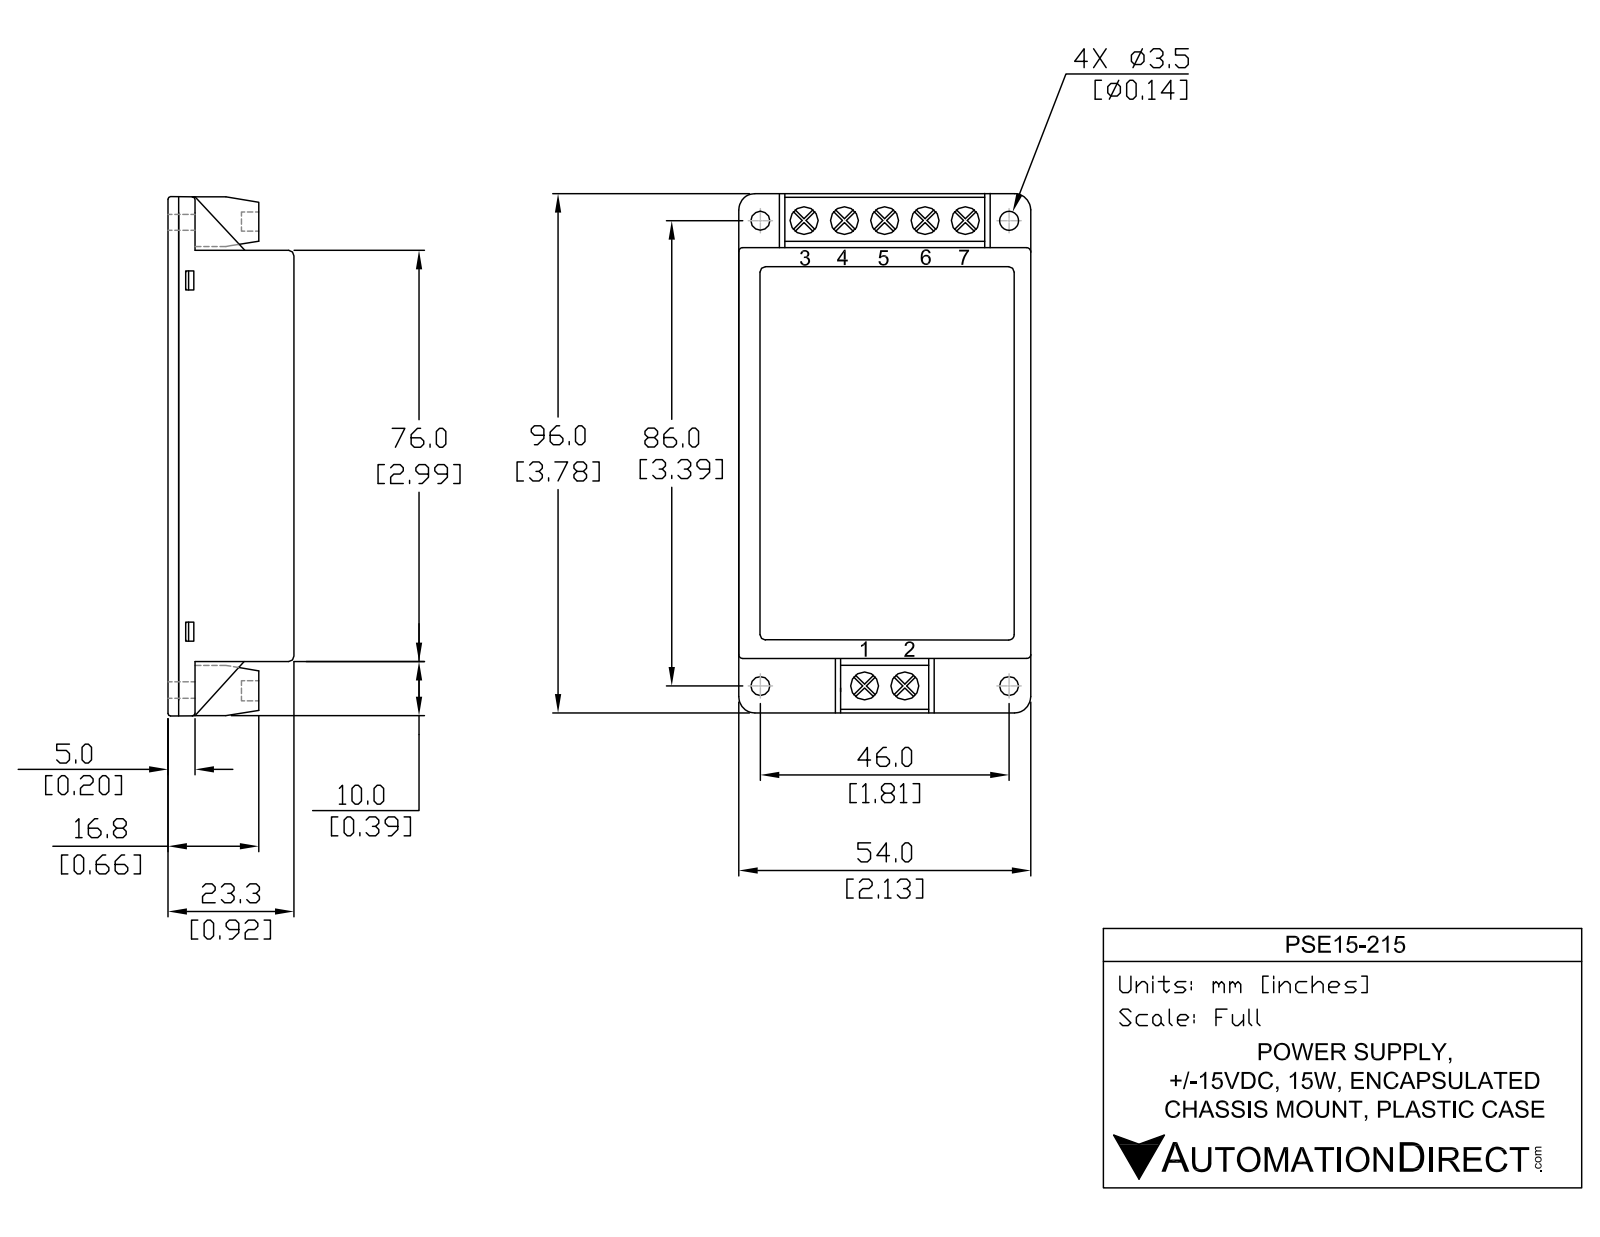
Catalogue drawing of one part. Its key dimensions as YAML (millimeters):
part_name: "PSE15-215"
step_written_by: "SolidWorks 2011 (CONFIG_CONTROL_DESIGN)"
units: millimeters
bodies: {solids: 2, faces: 369, planar: 246, cylindrical: 62, other: 61}
overall_size: [96, 54.1, 23.4]
volume: 105900
surface_area: 29380
round_holes:
  - {diameter: 5.1, count: 7}
  - {diameter: 3.6, count: 4}
partial_cylinders:
  - {radius: 0.8, count: 20}
  - {radius: 3.2, count: 4}
face_to_face_distances: [2, 2, 21.3, 23.3, 21.3, 54.1, 75.9, 23.4, 21.4, 0.4]
hole_center_spacings: [6.6, 13.2, 6.6, 19.7, 26.3, 46, 85.4, 85.4]
